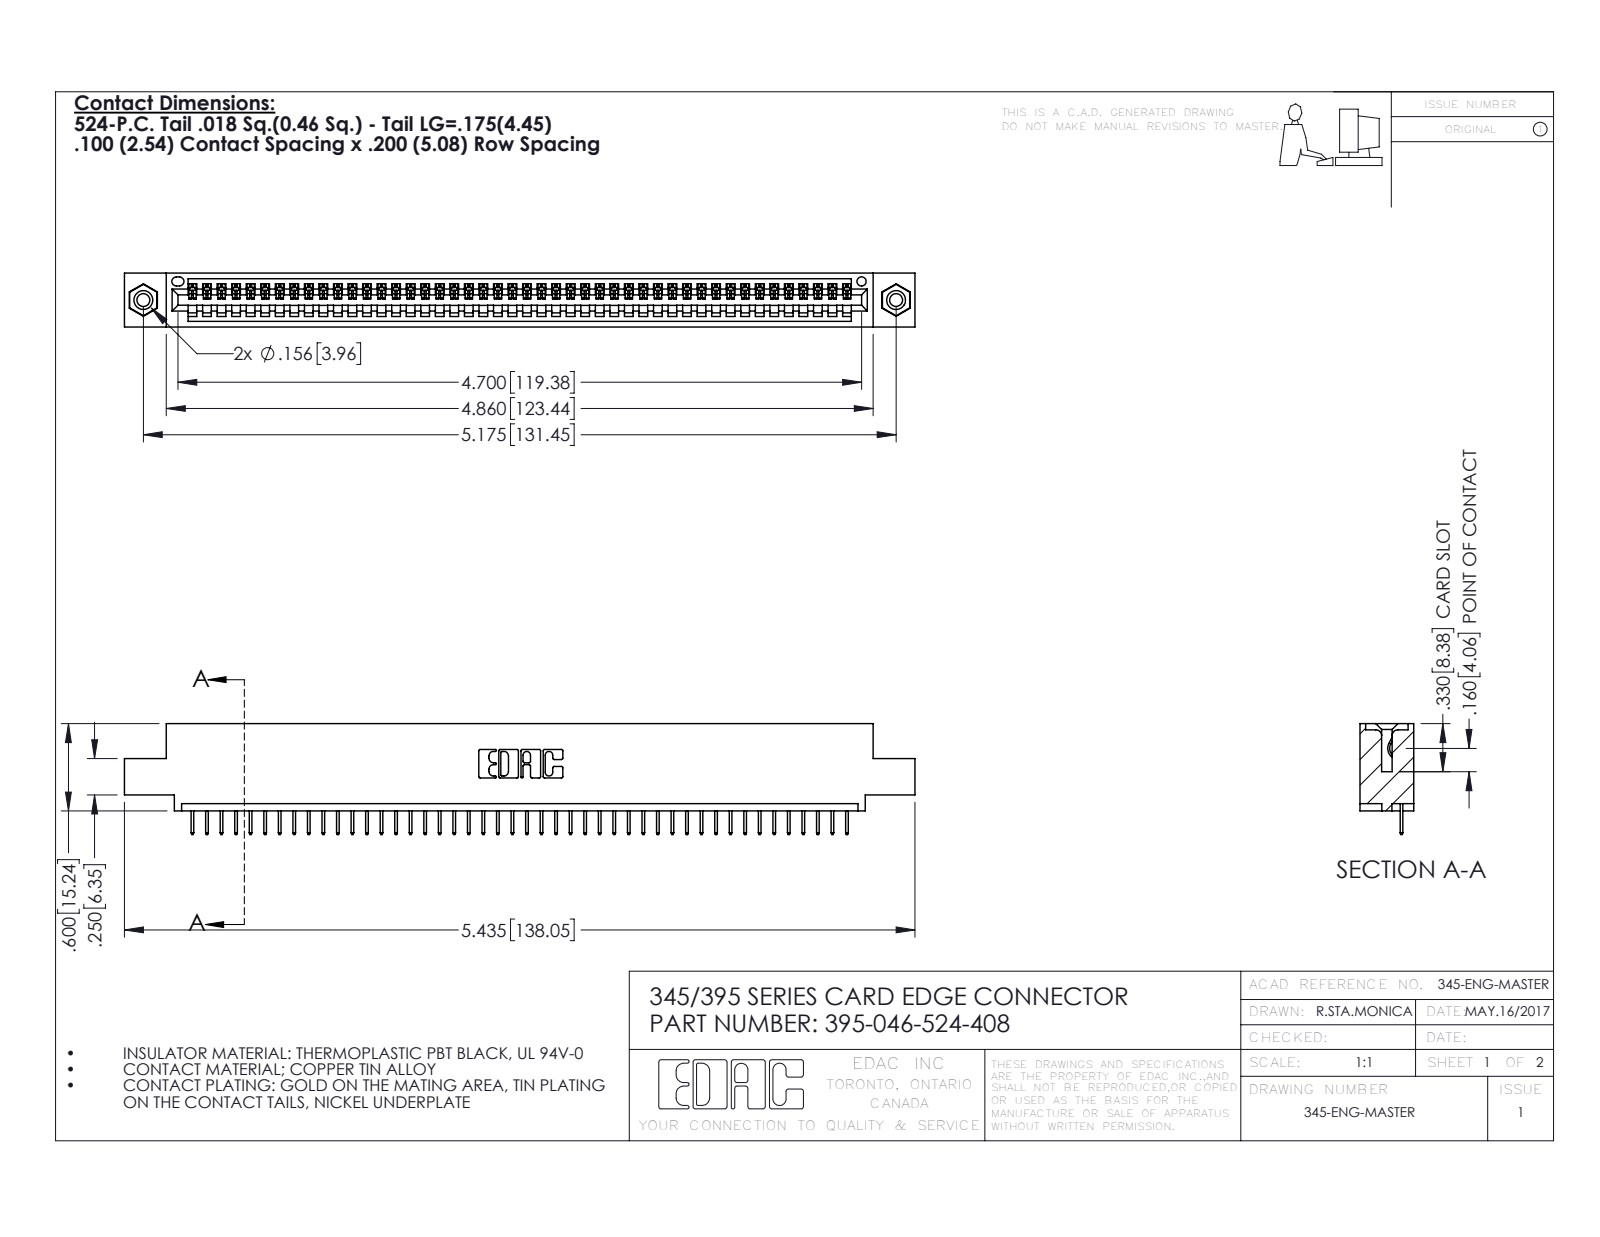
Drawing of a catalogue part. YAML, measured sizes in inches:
part_name: "345-250-001_345-250-003-102; 345-292-001_345-293-124; 395-046-524-408; 345 Part_0.110 Offset - 0.156 Dia-TI"
step_written_by: "SolidWorks 2016 (CONFIG_CONTROL_DESIGN)"
units: inches
bodies: {solids: 49, faces: 3042, planar: 2232, cylindrical: 794, other: 16}
overall_size: [5.435, 0.762, 0.37]
volume: 0.786
surface_area: 25.88
round_holes:
  - {diameter: 0.089, count: 2}
  - {diameter: 0.125, count: 2}
  - {diameter: 0.156, count: 2}
  - {diameter: 0.064, count: 1}
round_bosses_or_shafts:
  - {diameter: 0.155, count: 2}
partial_cylinders:
  - {radius: 0.006, count: 92}
  - {radius: 0.01, count: 22}
  - {radius: 0.007, count: 6}
  - {radius: 0.031, count: 6}
  - {radius: 0.026, count: 3}
  - {radius: 0.031, count: 2}
  - {radius: 0.04, count: 2}
  - {radius: 0.014, count: 1}
face_to_face_distances: [0.072, 0.298, 0.37, 0.2, 0.098, 0.272, 0.025, 0.225, 0.072, 0.149]
hole_center_spacings: [0.27, 4.939, 5.175]
